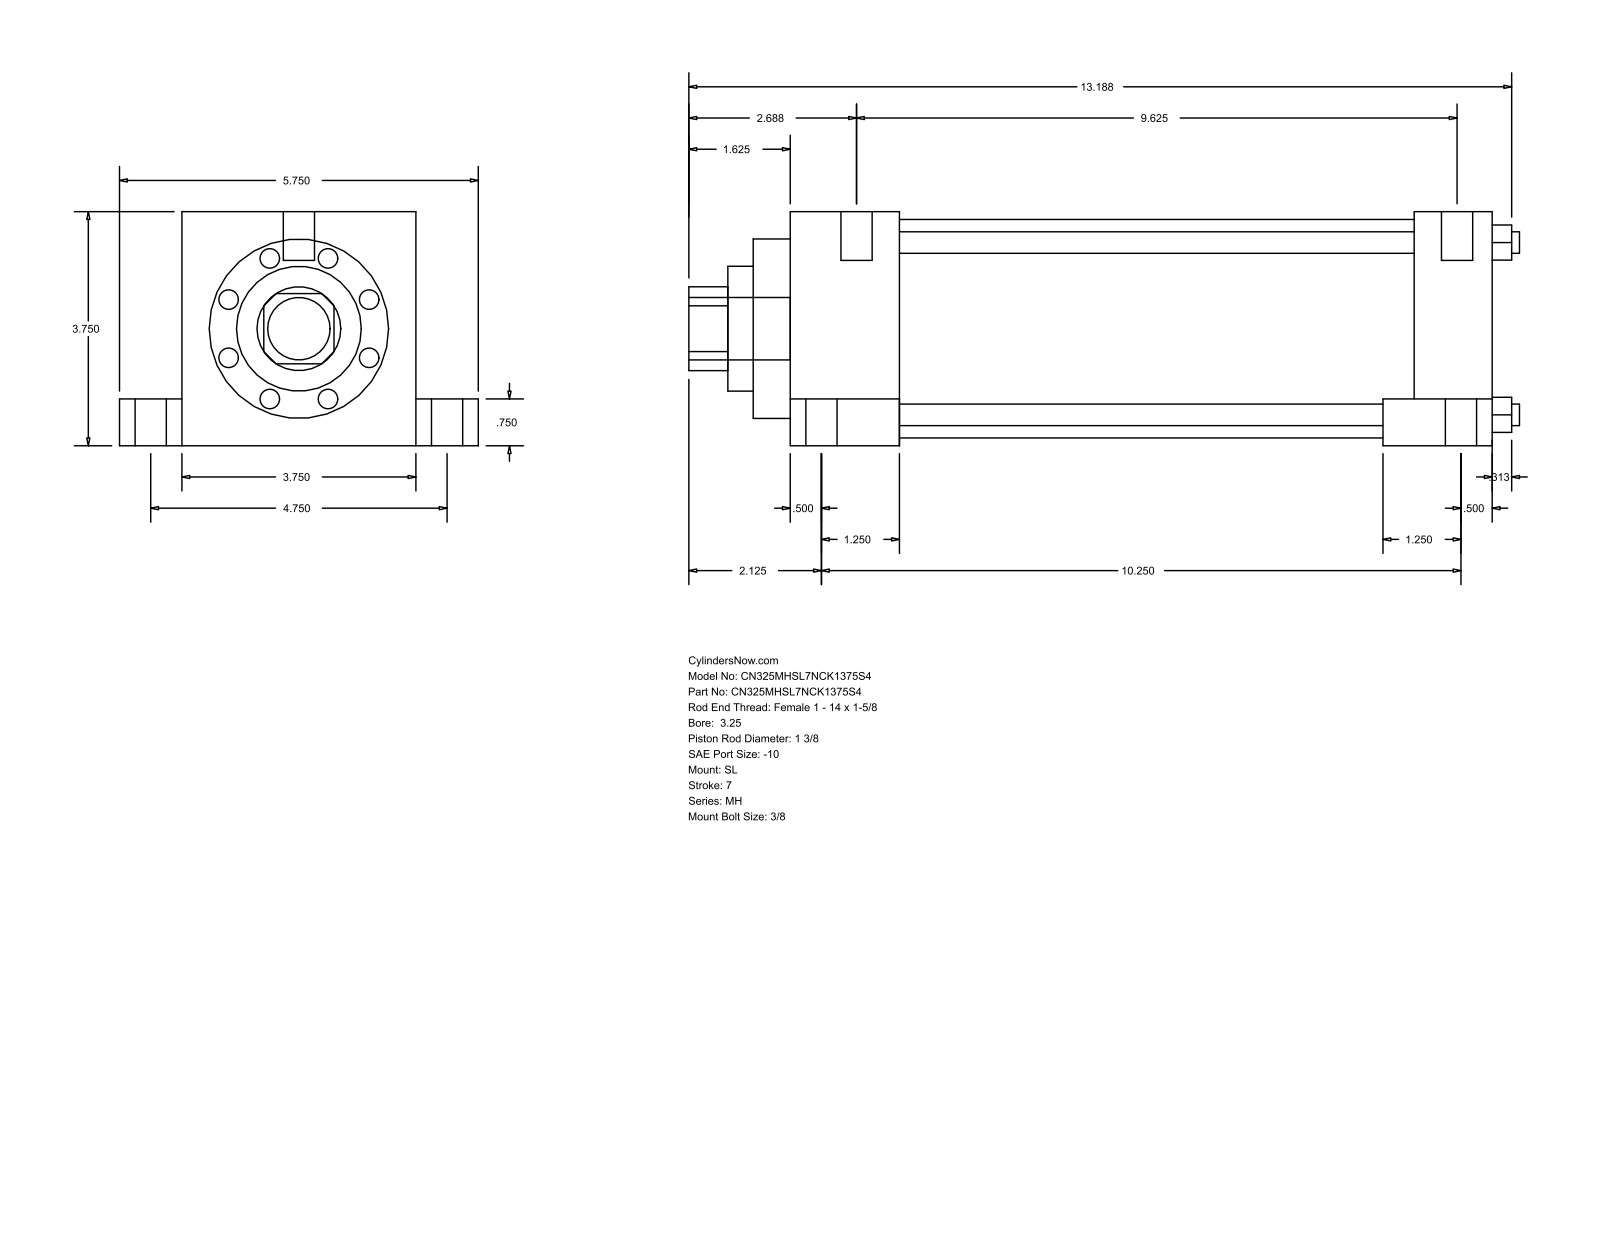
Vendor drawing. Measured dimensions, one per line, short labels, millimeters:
name: MH_SL__0325_1.375
written by: GSSL Pune (CONFIG_CONTROL_DESIGN)
unit: mm
bodies: 0 solids, 110 faces (77 planar, 33 cylindrical, 0 other)
size: 338.14 × 146.05 × 95.25
holes: 4× ⌀8.76, 1× ⌀34.92, 1× ⌀50.8, 1× ⌀73.03, 1× ⌀88.9
bosses: 6× ⌀12.7, 4× ⌀19.05, 4× ⌀5.56, 1× ⌀25.4
rounds: 1× R17.06
face distances: 95.24, 285.75, 44.45, 241.3, 25.41, 120.65, 19.05, 76.19, 254, 209.55
hole spacings: 49.57, 70.1, 99.14
